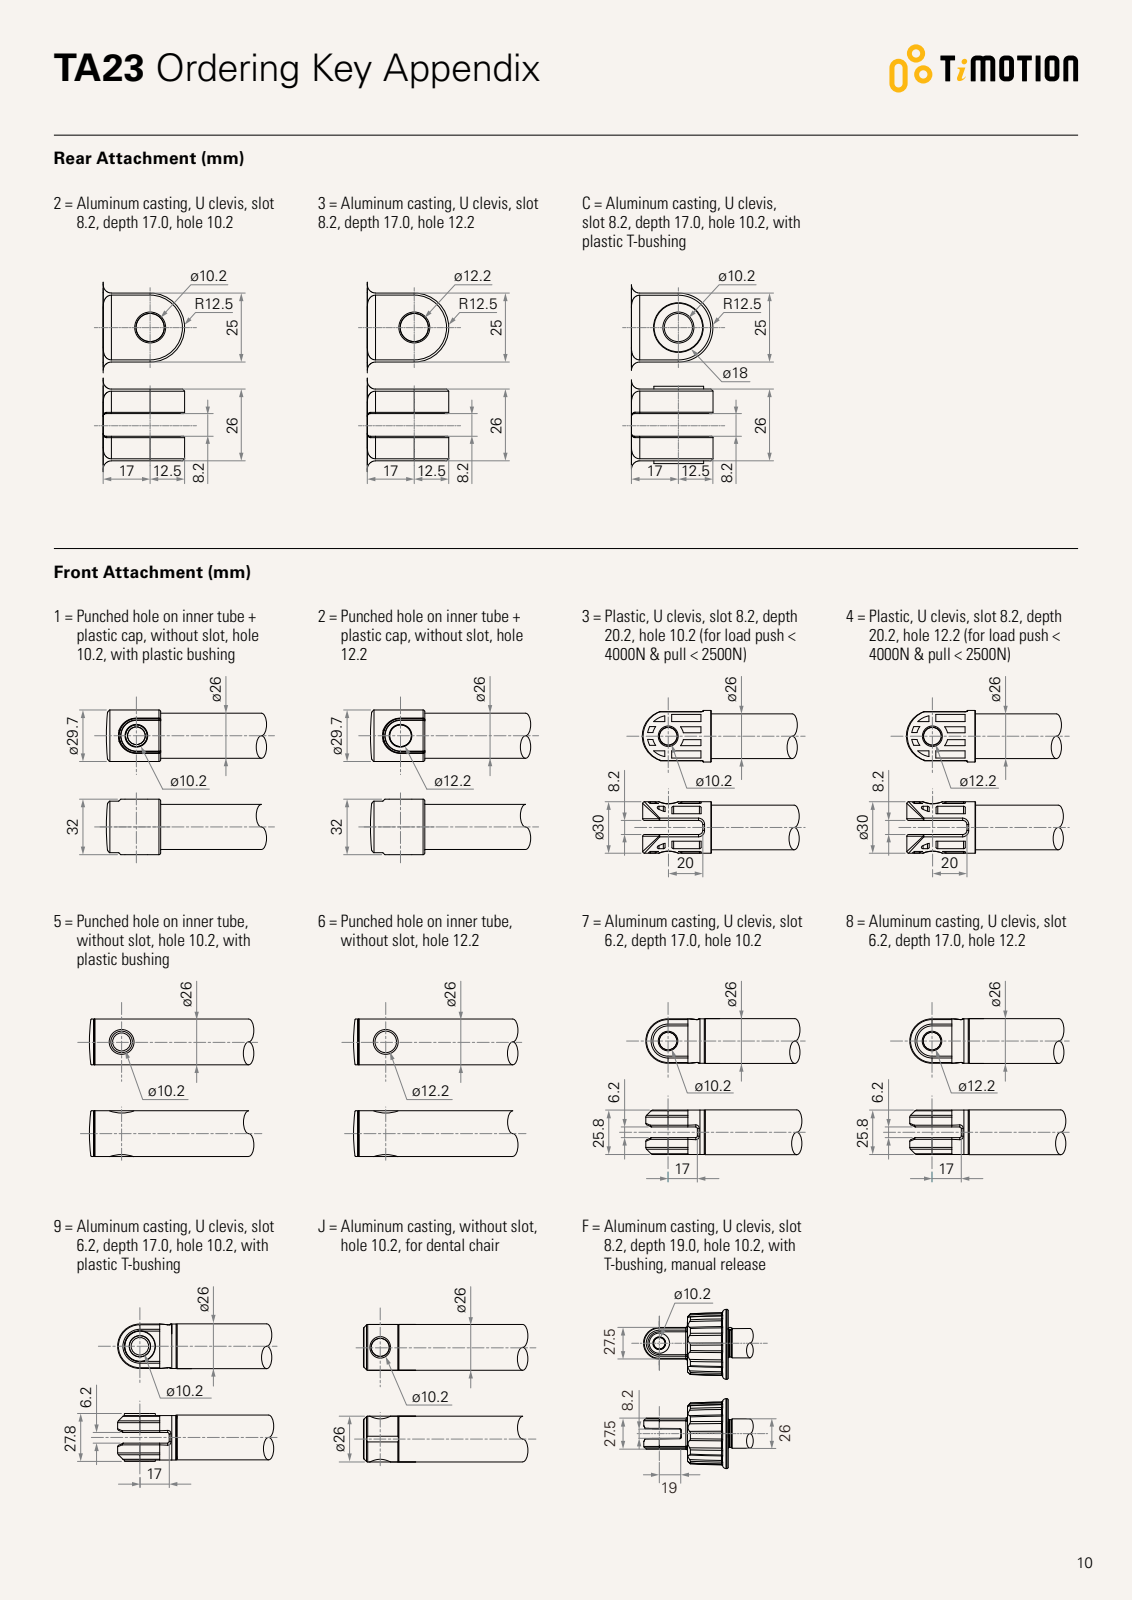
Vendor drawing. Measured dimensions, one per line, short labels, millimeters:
name: TA23
written by: SolidWorks 2015 (CONFIG_CONTROL_DESIGN)
unit: mm
bodies: 3 solids, 358 faces (69 planar, 105 cylindrical, 184 other)
size: 313.8 × 162.19 × 88.1
volume: 1 034 000 mm³; area: 103 365 mm²
holes: 7× ⌀7.8, 1× ⌀10.2, 1× ⌀12.5, 1× ⌀21
bosses: 1× ⌀29.7, 1× ⌀26, 1× ⌀18, 1× ⌀7.8, 1× ⌀5
rounds: 16× R0.5, 8× R3, 6× R1, 2× R4, 2× R6, 2× R7, 2× R8, 2× R60
face distances: 25, 4.1, 13, 2, 169.6, 10.5, 8.9, 17.1, 41.8, 211.4
hole spacings: 34.21, 36.07, 36.31, 37.05, 37.72, 38.67, 44.8, 46.05
